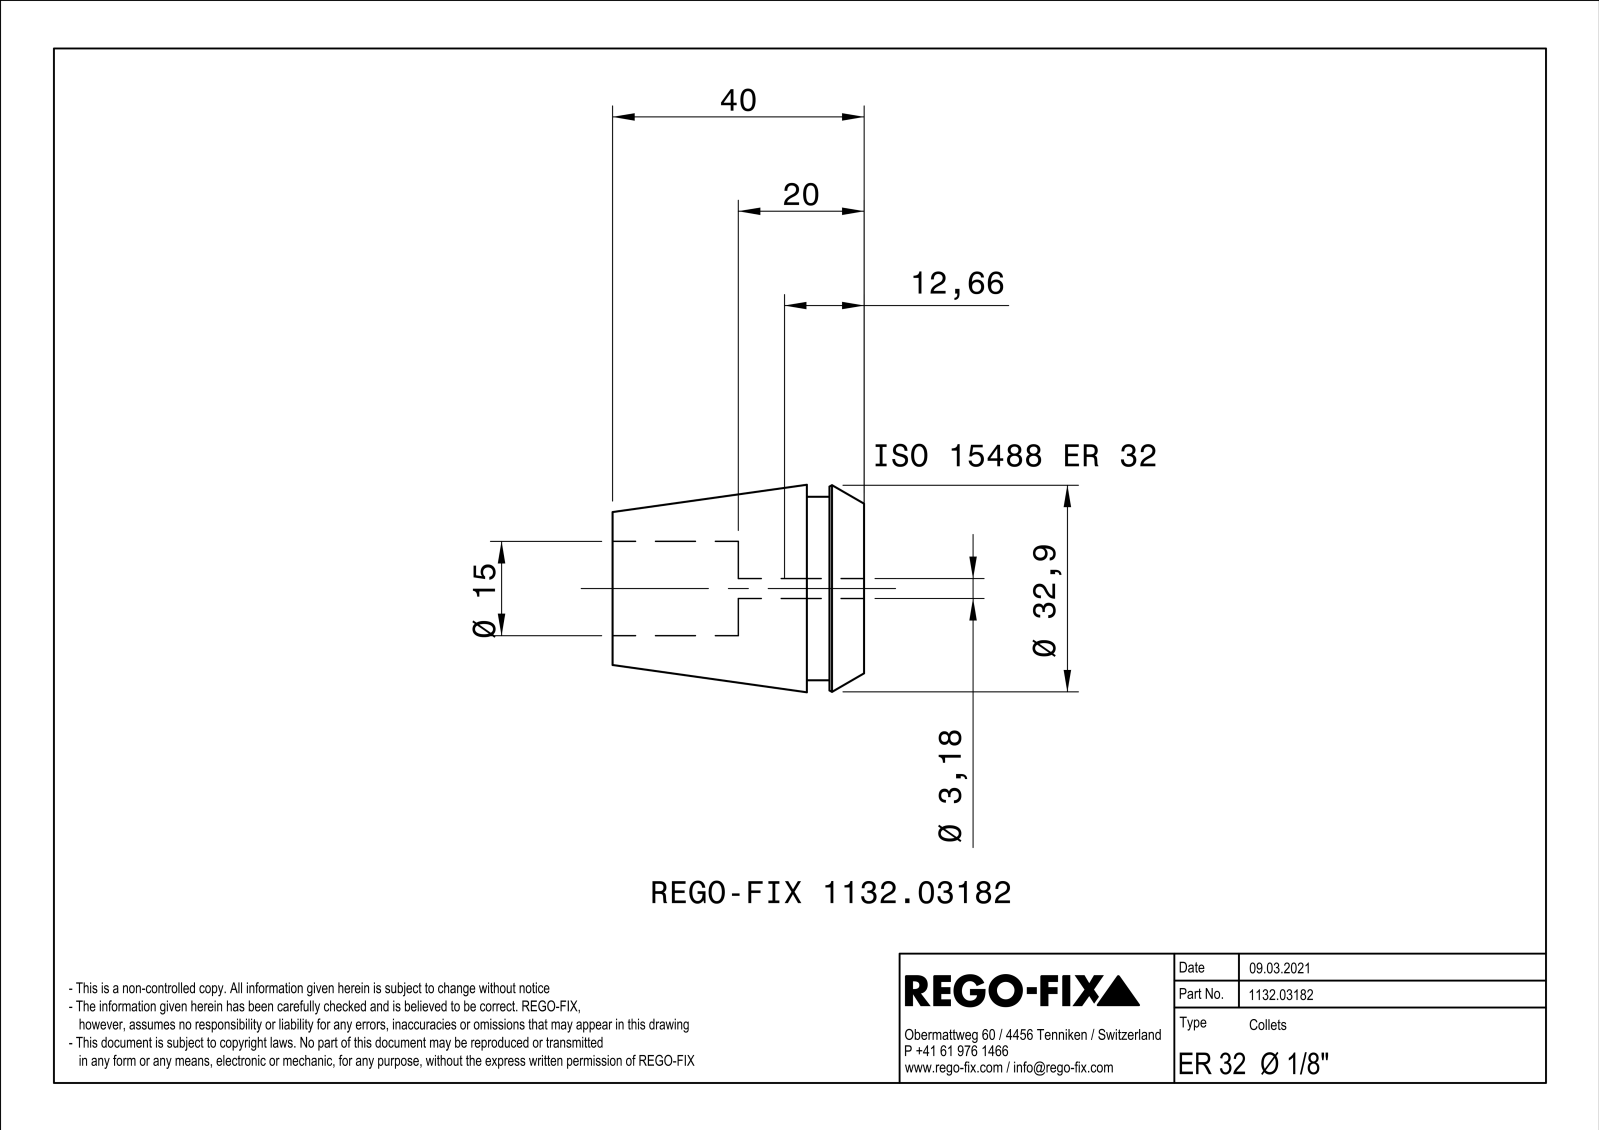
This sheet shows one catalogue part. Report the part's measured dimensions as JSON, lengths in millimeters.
{"part_name": "NOCUT", "step_written_by": "SIEMENS PLM Software Solid Edge ST10 (AUTOMOTIVE_DESIGN)", "units": "millimeters", "bodies": {"solids": 1, "faces": 256, "planar": 88, "cylindrical": 48, "other": 120}, "overall_size": [40, 32.99, 32.99], "volume_mm3": 19893, "surface_area_mm2": 14960, "round_holes": [[15, 1]], "round_bosses_or_shafts": [[29.2, 1]], "partial_cylinders_radius": [[0.3, 13], [1.59, 1]], "face_to_face_distances": [0.6, 0.62, 0.58, 40, 20, 9.1, 30.9, 5.5, 3.6, 34.5]}
